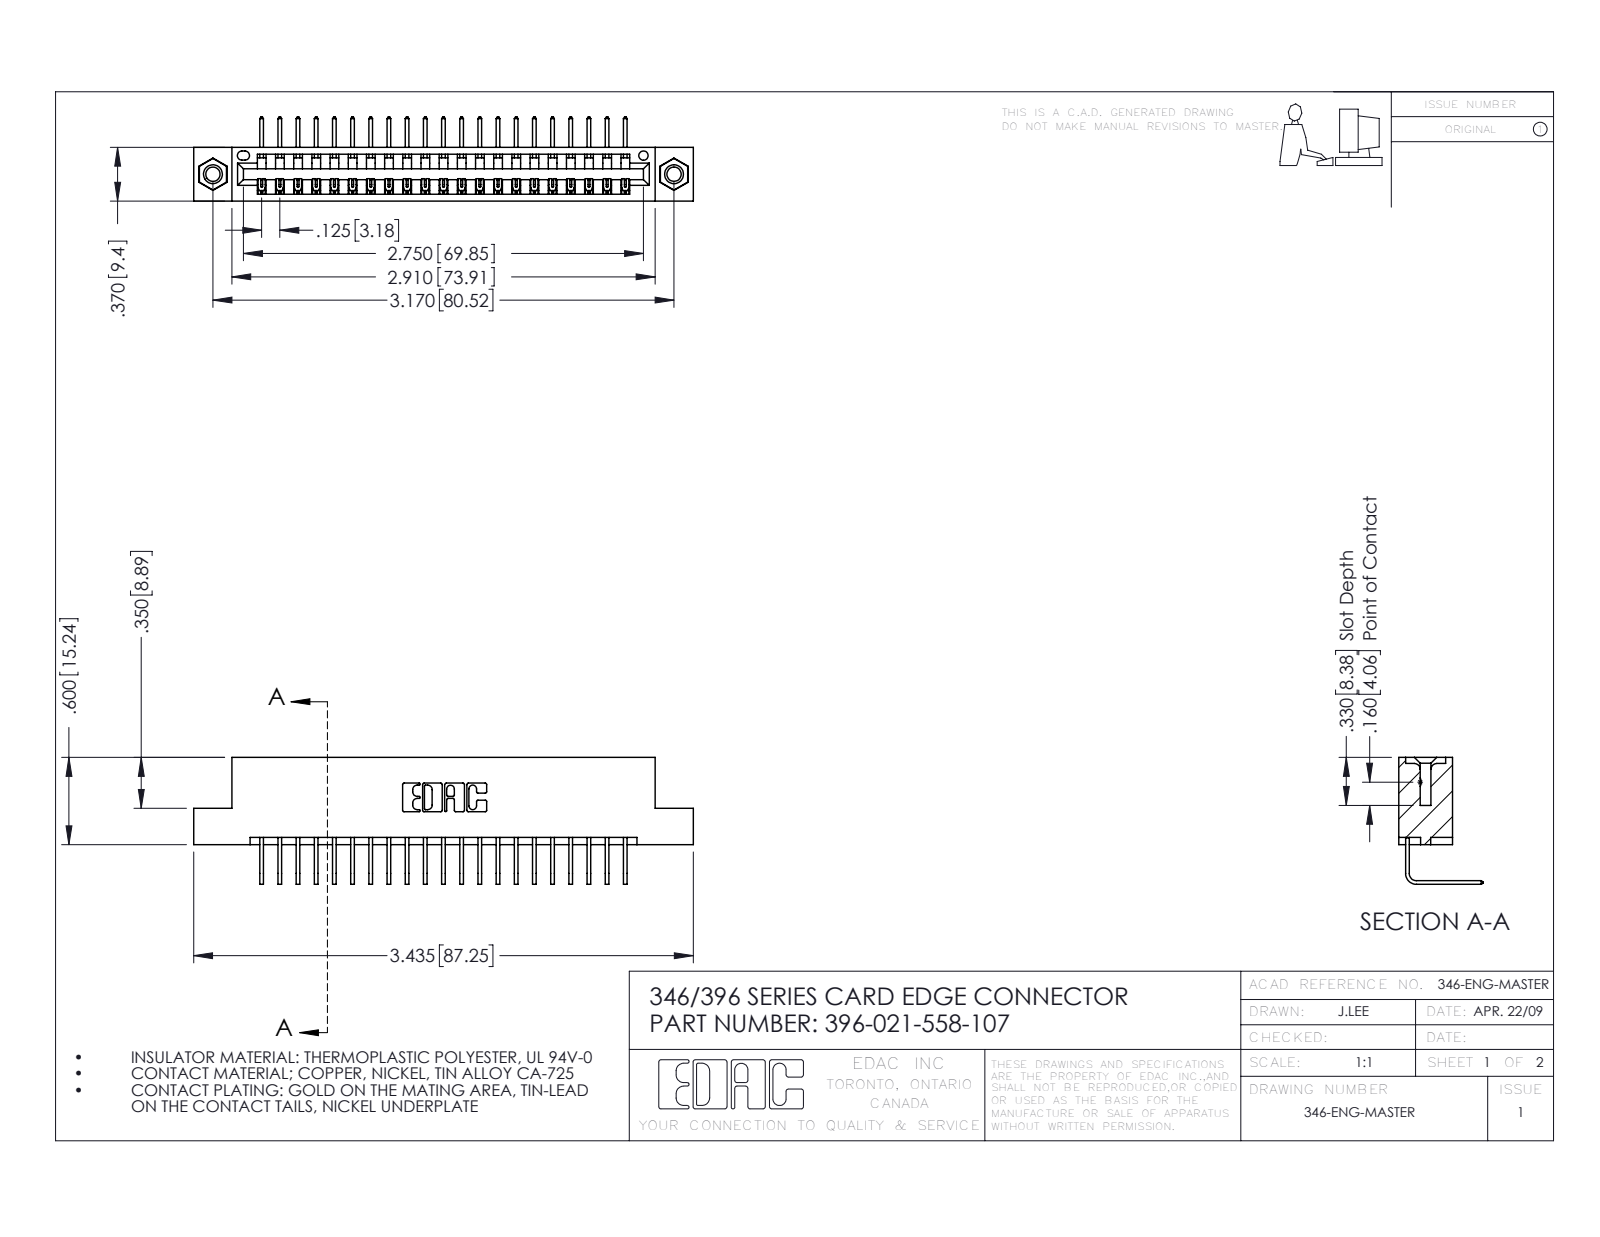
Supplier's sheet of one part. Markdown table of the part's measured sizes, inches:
| quantity | value |
| --- | --- |
| part name | 345-292-001_558 Tail - 2; 345-250-001_345-250-005-103; 396-021-558-107; 346 Part_Flush Mounting Lugs - 0.156 Dia-TI |
| STEP written by | SolidWorks 2016 (CONFIG_CONTROL_DESIGN) |
| units | inches |
| bodies | 24 solids, 1442 faces (990 planar, 436 cylindrical, 16 other) |
| overall size | 3.435 × 0.873 × 0.58 |
| volume | 0.504 in³ |
| surface area | 16.36 in² |
| round holes (diameter × count) | 0.098 × 2, 0.125 × 2, 0.156 × 2, 0.064 × 1 |
| round bosses / shafts (diameter × count) | 0.155 × 2 |
| partial cylindrical surfaces (radius × count) | 0.006 × 42, 0.01 × 22, 0.007 × 6, 0.031 × 6, 0.026 × 3, 0.031 × 2, 0.04 × 2, 0.014 × 1 |
| main face-to-face distances | 0.322, 0.048, 0.37, 0.25, 0.298, 0.025, 0.072, 0.148, 0.222, 0.1 |
| hole center spacings | 0.246, 2.963, 3.17 |
